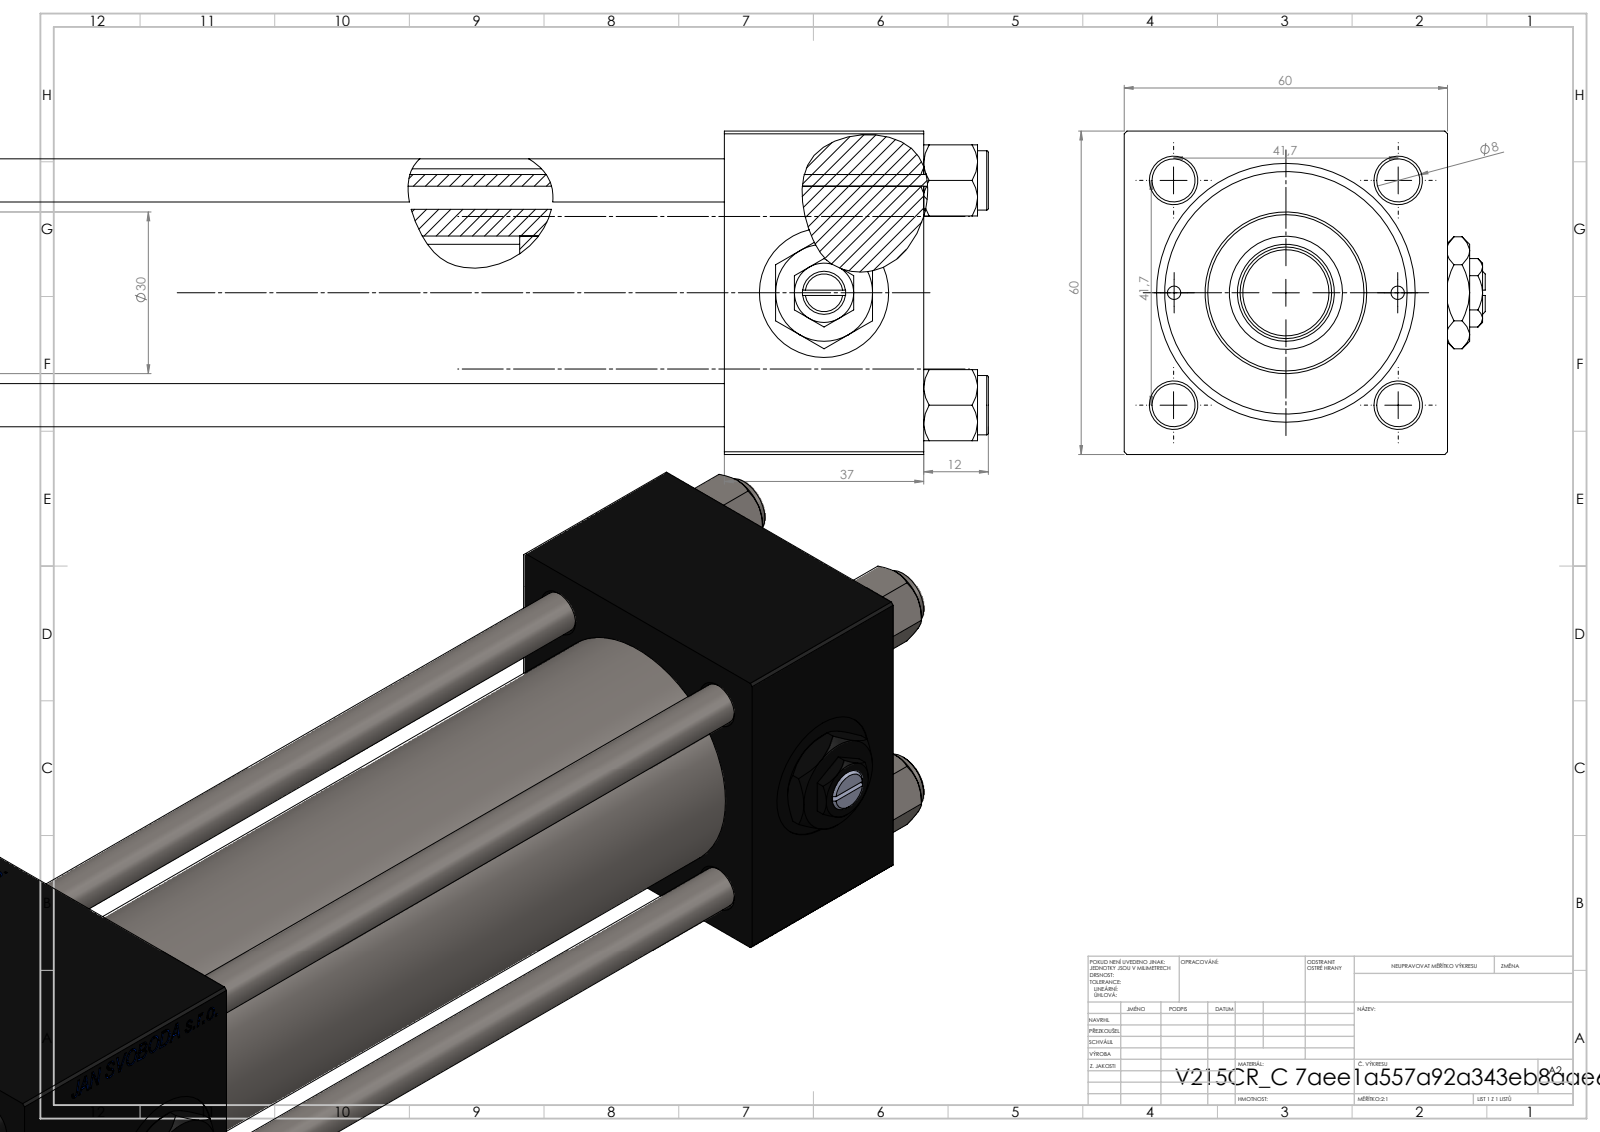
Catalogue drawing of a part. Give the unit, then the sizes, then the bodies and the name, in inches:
Units: inches
Overall size (bounding box): 11.22 × 2.638 × 2.362
Round holes (diameter × count): ⌀0.315 ×4, ⌀0.098 ×2, ⌀0.276 ×2, ⌀0.656 ×2, ⌀0.945 ×2, ⌀0.335 ×1, ⌀0.709 ×1, ⌀0.827 ×1, ⌀1.22 ×1, ⌀1.575 ×1, ⌀1.772 ×1
Round bosses / shafts (diameter × count): ⌀0.433 ×5, ⌀1.811 ×1, ⌀1.181 ×1, ⌀0.669 ×1
Main face-to-face distances: 2.362, 1.457, 8.976, 7.52, 2.087, 6.89, 5.433, 7.846, 6.39, 0.957
Hole centre spacings: 0.821, 1.161, 1.642, 1.832, 0.817, 2.322, 1.634, 6.791
Volume: 28.76 in³ · Surface area: 222.9 in²
Bodies: 14 solids, 1267 faces (579 planar, 106 cylindrical, 582 other)
Part name (STEP PRODUCT): V215CR_VCP_C; V215CR_C_TYCINKA; V215CR_C_Body; NUT_M5_C (+3 more)
STEP written by: SolidWorks 2019 (CONFIG_CONTROL_DESIGN)
